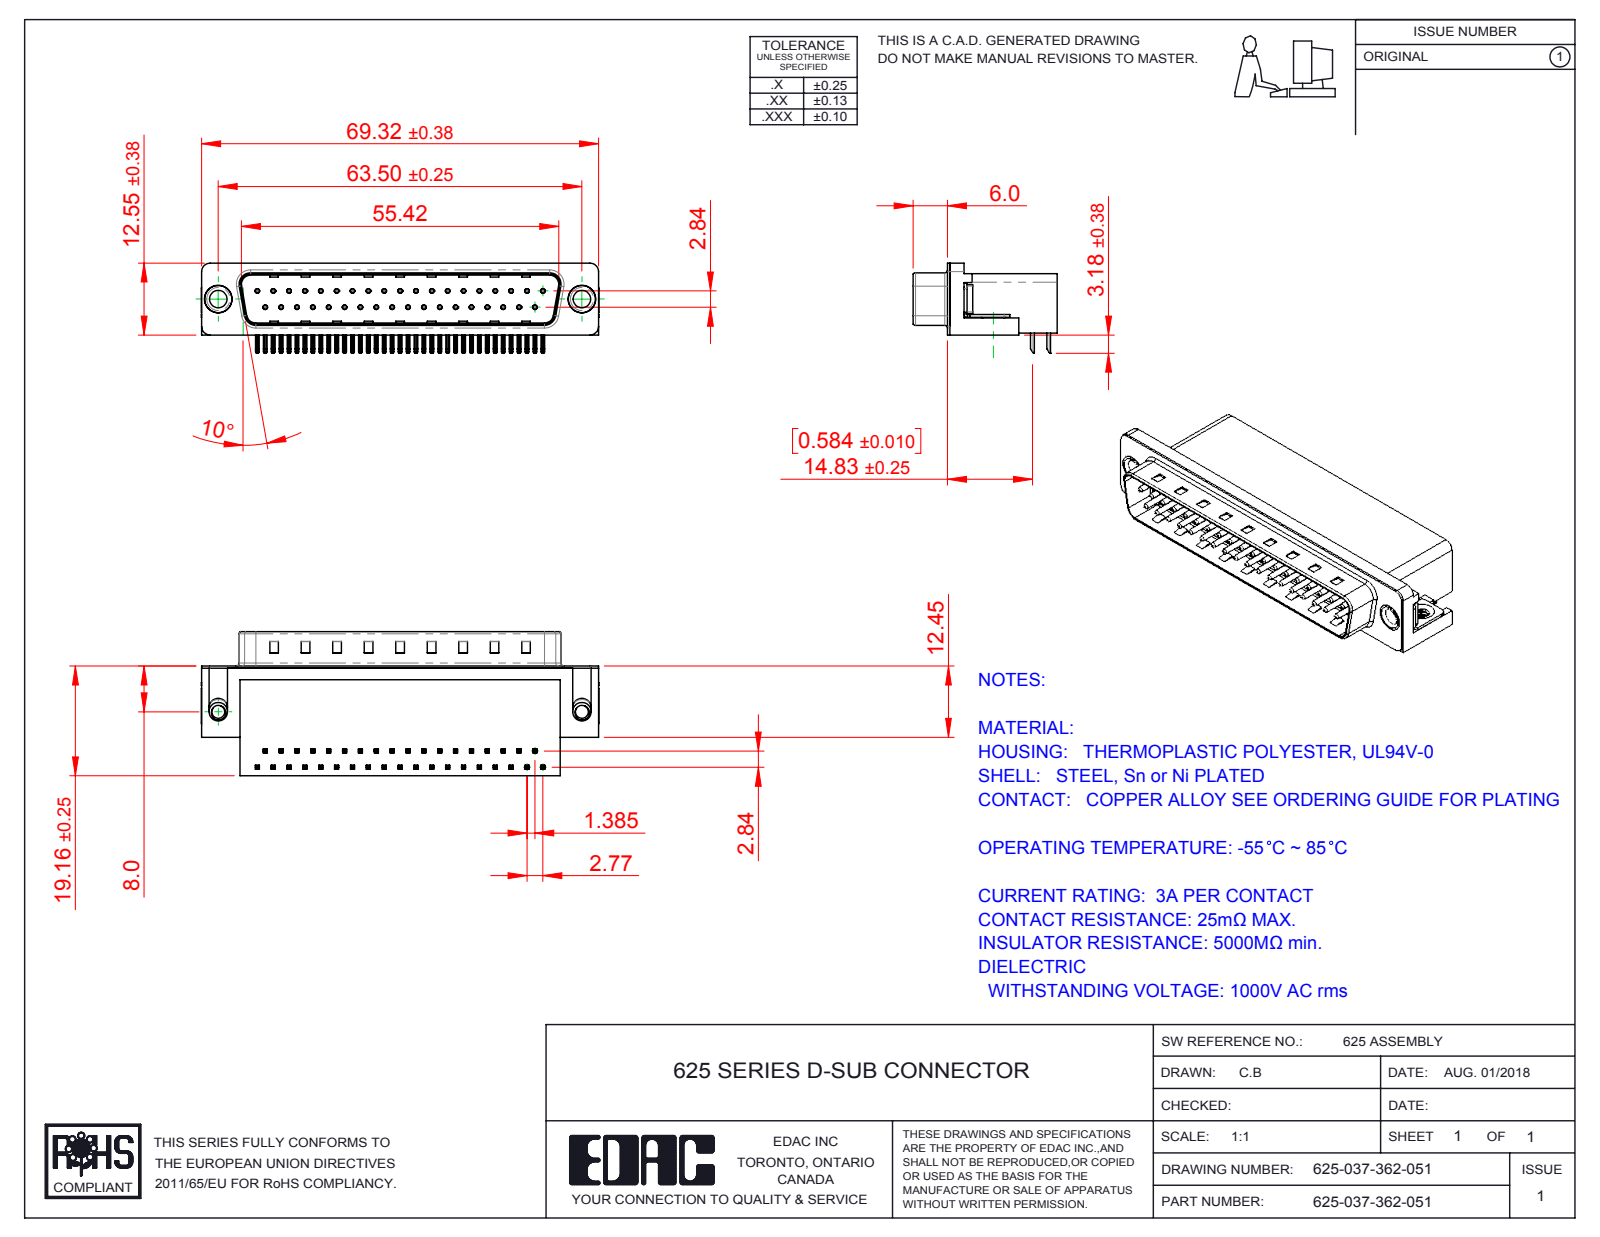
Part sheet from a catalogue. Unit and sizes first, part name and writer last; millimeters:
Units: millimetres
Overall size (bounding box): 69.4 × 25.16 × 15.73
Round holes (diameter × count): ⌀0.35 ×37, ⌀0.8 ×37, ⌀2.26 ×2, ⌀3.05 ×2, ⌀4 ×2, ⌀4.8 ×2, ⌀5 ×2
Round bosses / shafts (diameter × count): ⌀0.75 ×37, ⌀4.9 ×2, ⌀4.75 ×2, ⌀3.85 ×2, ⌀3.26 ×2
Partial cylindrical surfaces — rounded edges, fillets, slot ends (radius × count): R0.25 ×156, R0.12 ×74, R1 ×16, R0.5 ×9, R1.6 ×8, R1.5 ×7, R0.9 ×4, R2 ×4
Main face-to-face distances: 10.34, 0.4, 18.76, 8.76, 19.16, 2.84, 2.09, 10.1, 1.74, 8.36
Hole centre spacings: 3.16, 2.77, 5.54, 8.31, 11.08, 13.85, 19.39, 22.16
Volume: 12 599 mm³ · Surface area: 11 810 mm²
Bodies: 43 solids, 3193 faces (2015 planar, 911 cylindrical, 267 other)
Part name (STEP PRODUCT): 625 Contact Bottom; 625 Contact Top; 625 Shell_37 Socket; 625-037-362-051 (+3 more)
STEP written by: SolidWorks 2016 (CONFIG_CONTROL_DESIGN)
